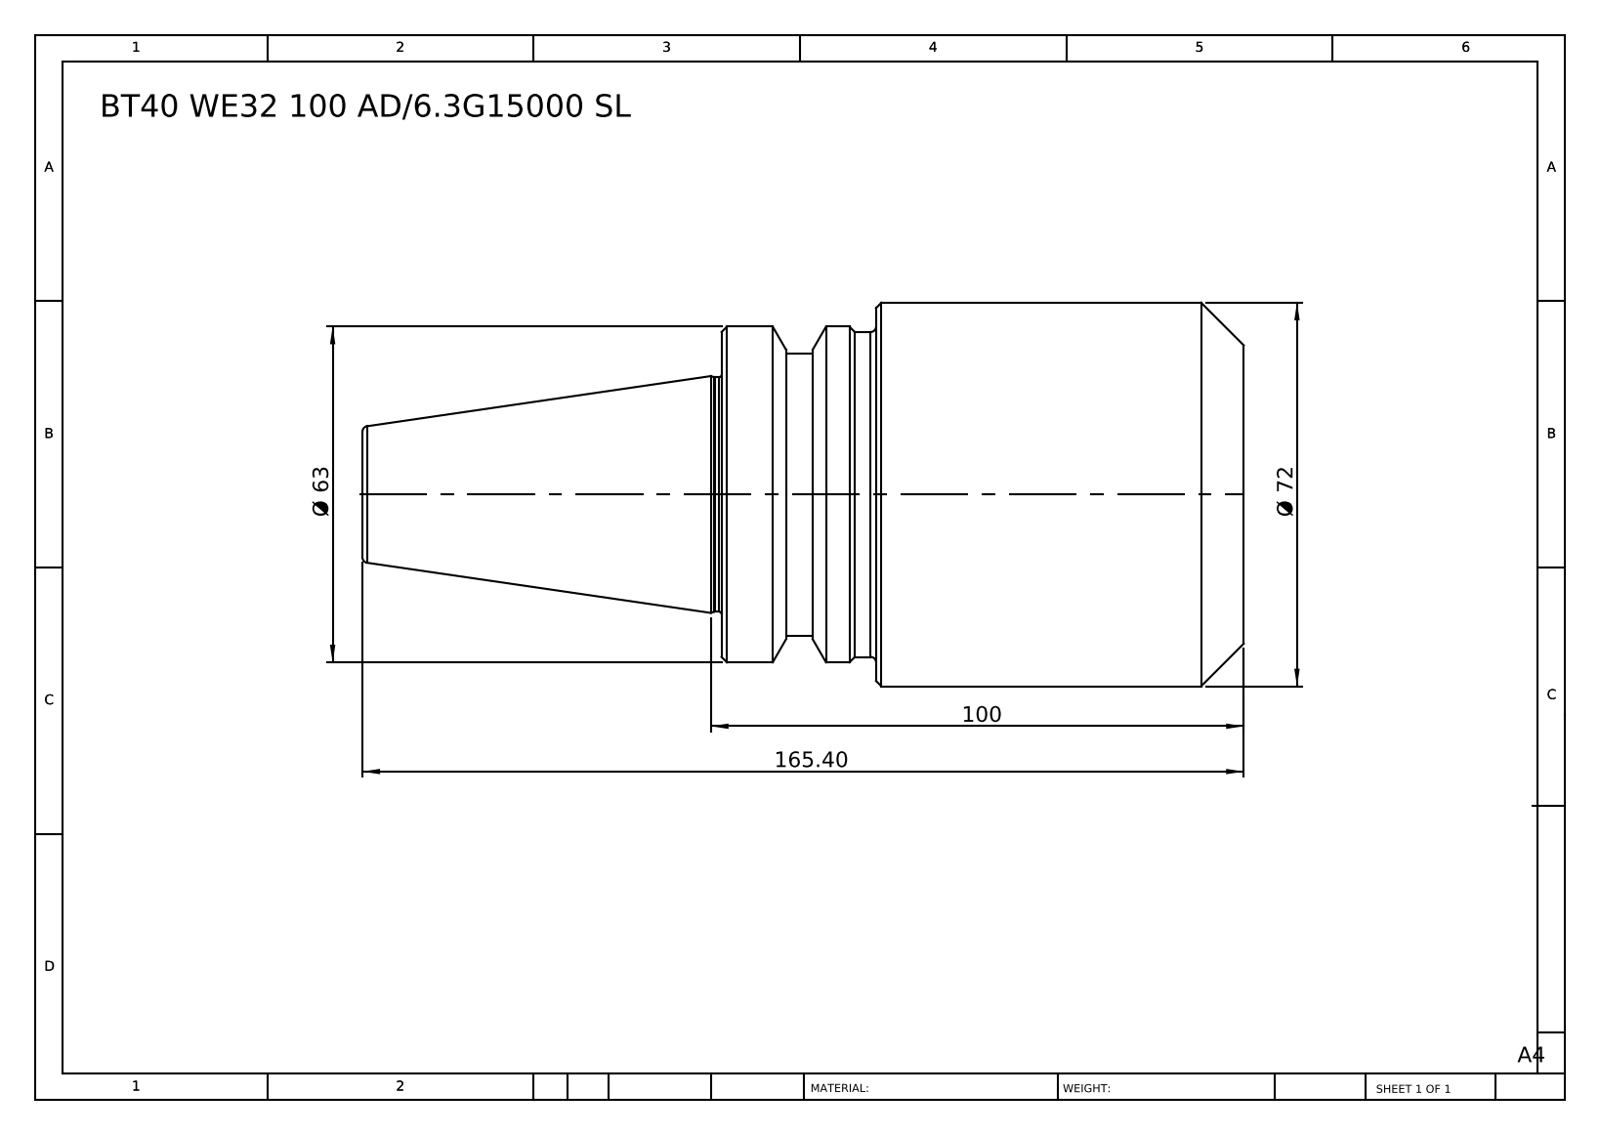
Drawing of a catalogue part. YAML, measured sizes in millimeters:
part_name: "BT40 WE32 100 AD-6.3G15000 SL"
step_written_by: "SolidWorks 2014 (CONFIG_CONTROL_DESIGN)"
units: millimeters
bodies: {solids: 1, faces: 42, planar: 6, cylindrical: 12, other: 24}
overall_size: [165.4, 72, 72]
volume: 424198
surface_area: 35646
round_bosses_or_shafts:
  - {diameter: 72, count: 1}
  - {diameter: 63, count: 1}
  - {diameter: 61, count: 1}
  - {diameter: 53, count: 1}
  - {diameter: 44, count: 1}
face_to_face_distances: [98, 69, 29, 165.4, 96.4, 67.4, 85.9, 16.9, 12.1, 79.5]
